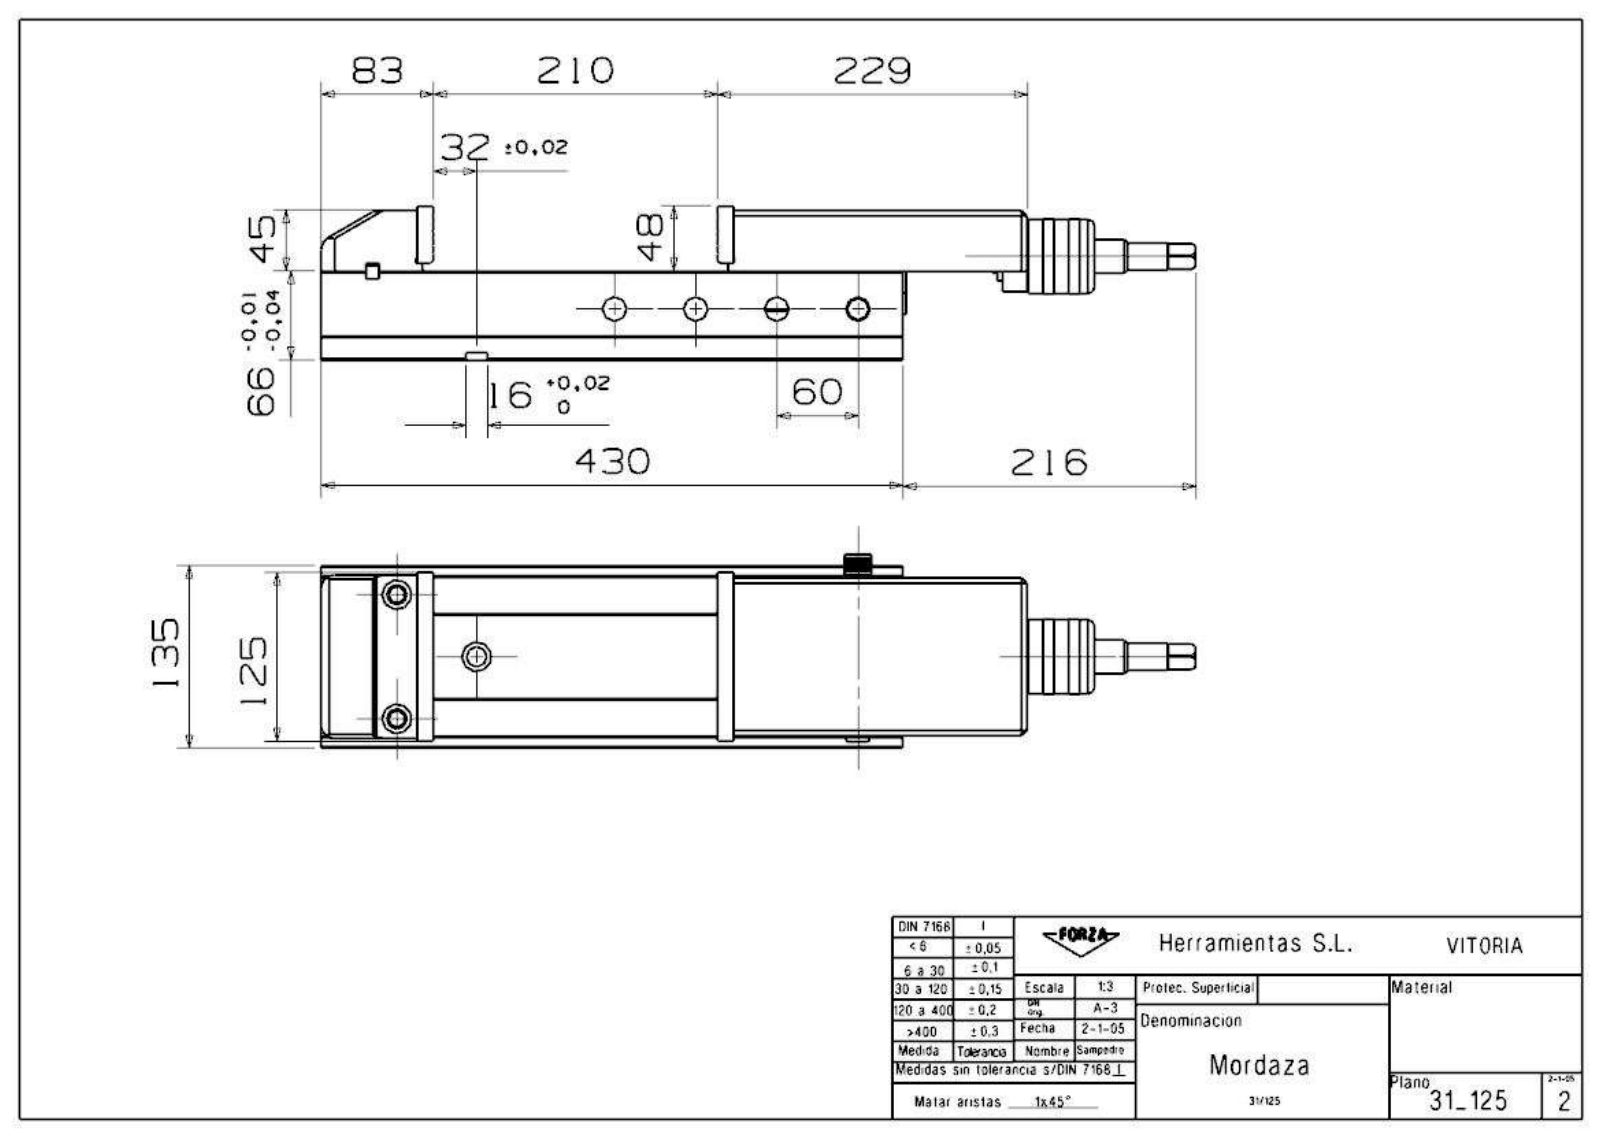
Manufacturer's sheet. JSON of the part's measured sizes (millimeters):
{"part_name": "31_125_Mordaza", "step_written_by": "SIEMENS PLM Software NX 7.5 (AUTOMOTIVE_DESIGN)", "units": "millimeters", "bodies": {"solids": 18, "faces": 550, "planar": 355, "cylindrical": 111, "other": 84}, "overall_size": [646.5, 143.5, 114], "volume_mm3": 3901000, "surface_area_mm2": 575726, "round_holes": [[15, 6], [22, 6], [5.19, 4], [6.99, 4], [10, 4], [12.38, 4], [14, 4], [18, 4], [3.43, 2], [4, 2], [4.5, 2], [8.5, 2]], "round_bosses_or_shafts": [[20, 2], [55.5, 1], [55, 1], [50, 1], [46, 1], [35.9, 1], [25, 1], [23.9, 1]], "partial_cylinders_radius": [[0.8, 2], [3, 2], [8, 2], [10, 2], [2, 1], [12, 1], [25, 1]], "face_to_face_distances": [66, 25.7, 40.3, 45, 22, 111, 85.3, 1.5, 96.5, 29.5], "hole_center_spacings": [60, 16.38, 17.5, 17.76, 24, 28.69, 35, 35.39]}
